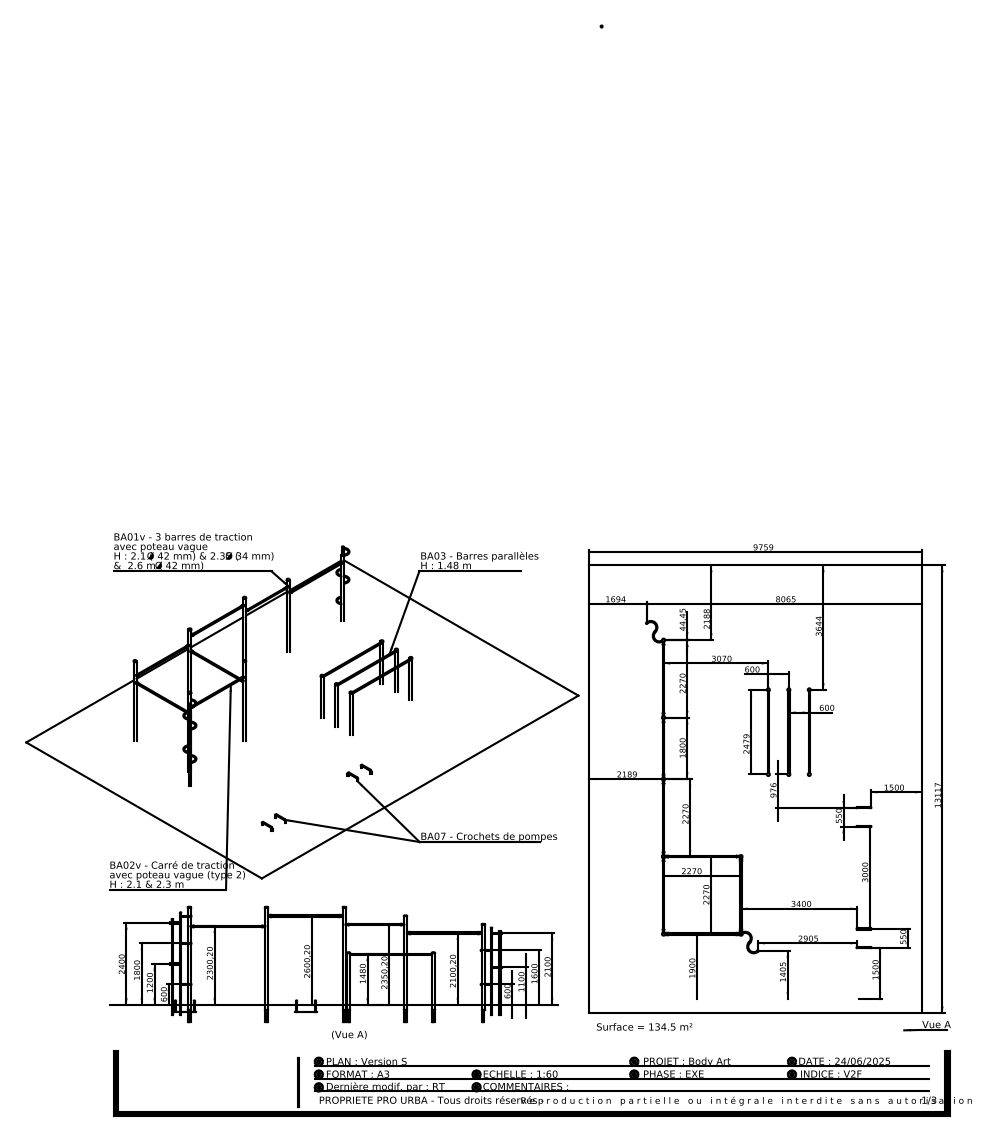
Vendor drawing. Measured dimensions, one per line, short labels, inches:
name: Traverse + visserie_Diam. 33.7; Poteau_Poteau double 180° - 2350 & 2600 avec diam33.7 sur h2300; Poteau_Poteau double 90° - 2100 & 2300 + vague 2; BA07 - Crochets de Pompes_BA07 V2 (+8 more)
written by: SolidWorks 2025 (AUTOMOTIVE_DESIGN)
unit: in
bodies: 139 solids, 2548 faces (832 planar, 900 cylindrical, 816 other)
size: 516.417 × 384.213 × 132.874
holes: 28× ⌀0.262, 28× ⌀0.315, 28× ⌀0.344, 28× ⌀0.354, 28× ⌀0.591, 13× ⌀3.343, 12× ⌀1.169, 10× ⌀0.787, 10× ⌀1.417, 9× ⌀1.709, 7× ⌀3.146, 7× ⌀3.303
bosses: 28× ⌀0.512, 13× ⌀3.5, 13× ⌀1.669, 13× ⌀1.327, 6× ⌀1.378, 1× ⌀1.063
face distances: 82.685, 7.874, 1.394, 90.559, 19.685, 2.362, 102.37, 9.843, 82.283, 3.74
hole spacings: 89.37, 5.121, 1.496, 2.795, 4.291, 85.125, 85.187, 86.62
